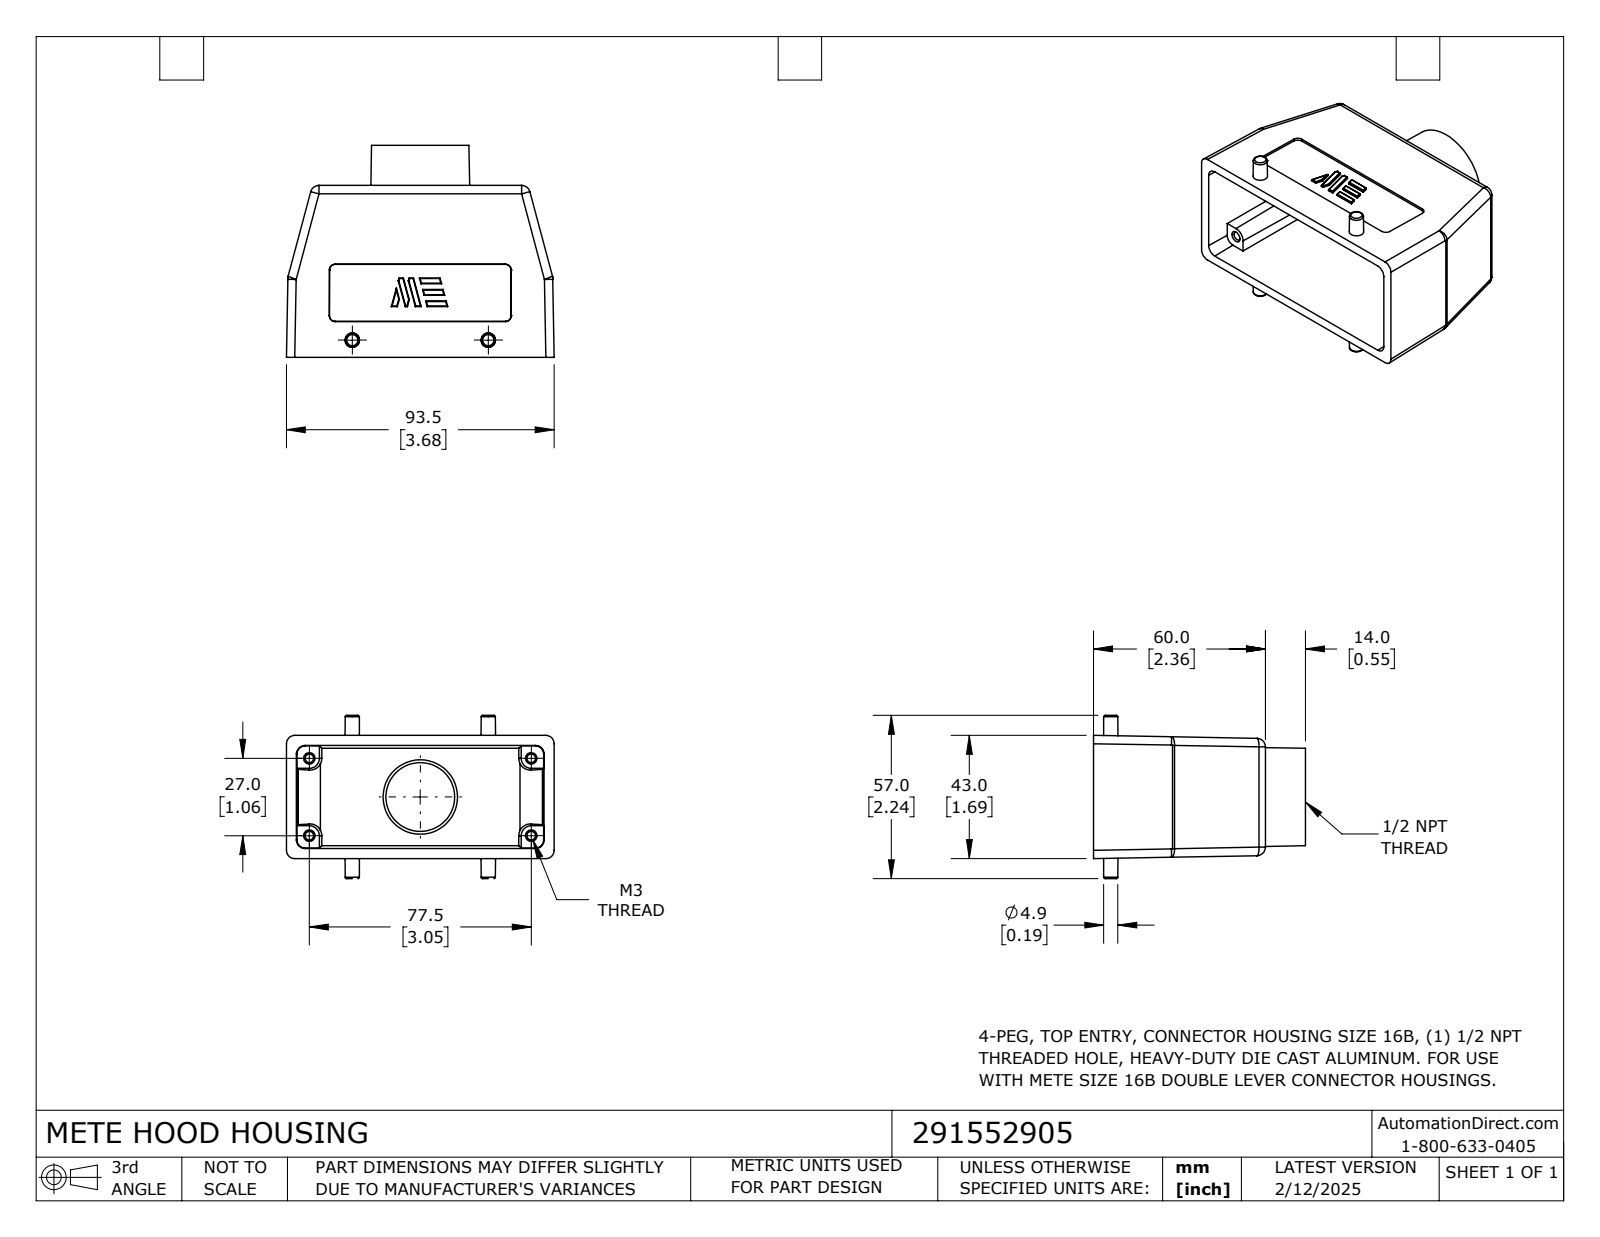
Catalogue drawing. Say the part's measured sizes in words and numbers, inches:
The part is named "291552905". Its 3-D file was written by "SolidWorks 2024 (CONFIG_CONTROL_DESIGN)". It is 1 solid with 247 faces: 113 planar, 90 cylindrical and 44 other. Overall it measures 3.681 by 2.913 by 2.244 inches. Its volume is 4.137 cubic inches and its surface area 58.97 square inches. Round holes: 4 of diameter 0.118, 1 of diameter 0.945, 1 of diameter 1.063. Partial cylindrical surfaces (rounded edges, fillets, slot ends): 35 of radius 0.008, 8 of radius 0.079, 8 of radius 0.118, 6 of radius 0.114, 2 of radius 0.098. The main face-to-face distances are 0.138, 0.031, 0.107, 0.118, 0.447, 0.309, 2.244, 2.362, 0.416, 2.913. The hole center spacings are 1.615, 1.063, 3.051, 3.231.
